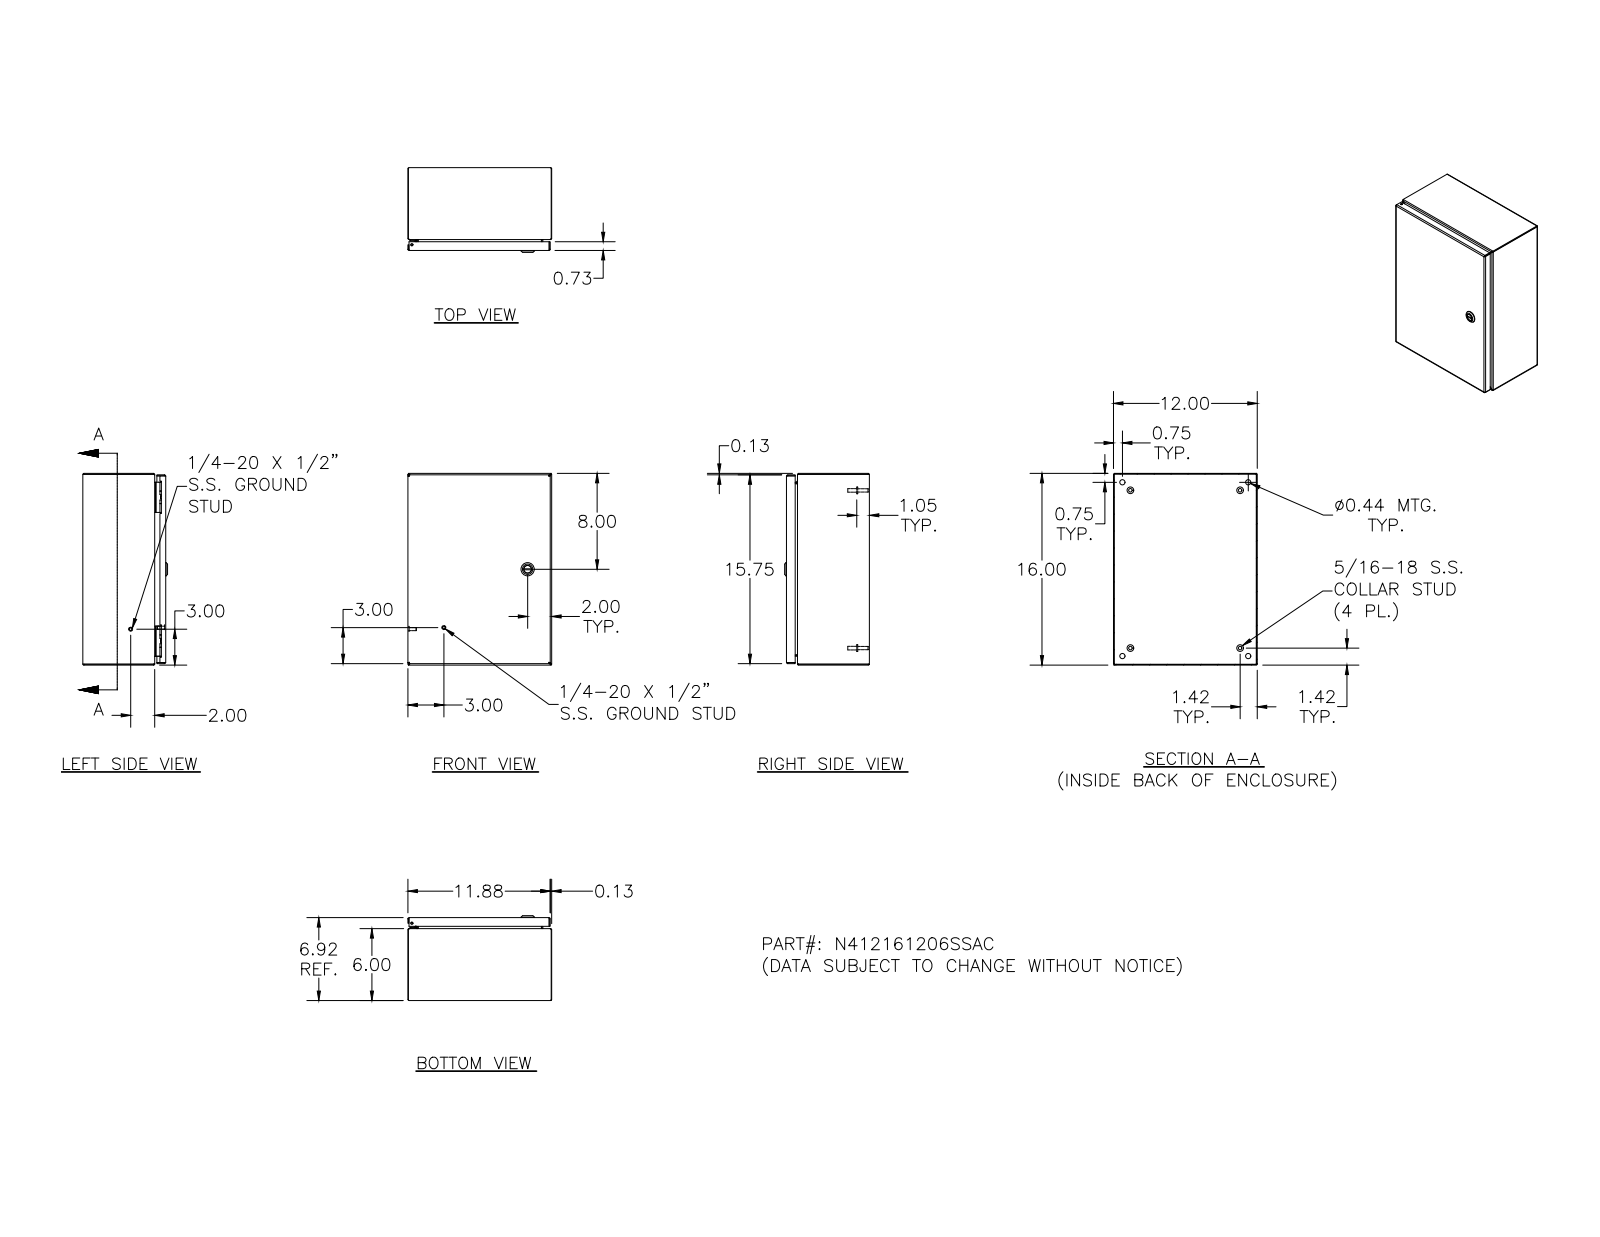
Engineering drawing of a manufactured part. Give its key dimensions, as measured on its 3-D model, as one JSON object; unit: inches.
{"part_name": "N412161206SSAC; N412161206SSACBKP; 388151; N4121612SSACLID (+8 more)", "step_written_by": "Autodesk Inventor 2011 (AUTOMOTIVE_DESIGN)", "units": "inches", "bodies": {"solids": 34, "faces": 1364, "planar": 523, "cylindrical": 497, "other": 344}, "overall_size": [16, 12, 7.075], "volume_in3": 62.32, "surface_area_in2": 1699, "round_holes": [[0.188, 5], [0.093, 4], [0.152, 4], [0.167, 4], [0.172, 4], [0.437, 4], [0.156, 2], [0.187, 1], [0.197, 1], [0.315, 1], [0.394, 1], [0.402, 1]], "round_bosses_or_shafts": [[0.25, 10], [0.563, 4], [0.36, 4], [0.32, 4], [0.3, 4], [0.275, 4], [0.256, 4], [0.164, 4]], "partial_cylinders_radius": [[0.05, 26], [0.016, 18], [0.016, 16], [0.09, 16], [0.031, 14], [0.125, 14], [0.02, 9], [0.032, 8]], "face_to_face_distances": [0.074, 6.843, 11.926, 6.769, 6.917, 15.926, 12, 11.852, 5.926, 0.917], "hole_center_spacings": [12, 0.017, 0.66, 0.019, 0.5, 0.648, 0.652, 0.656]}
